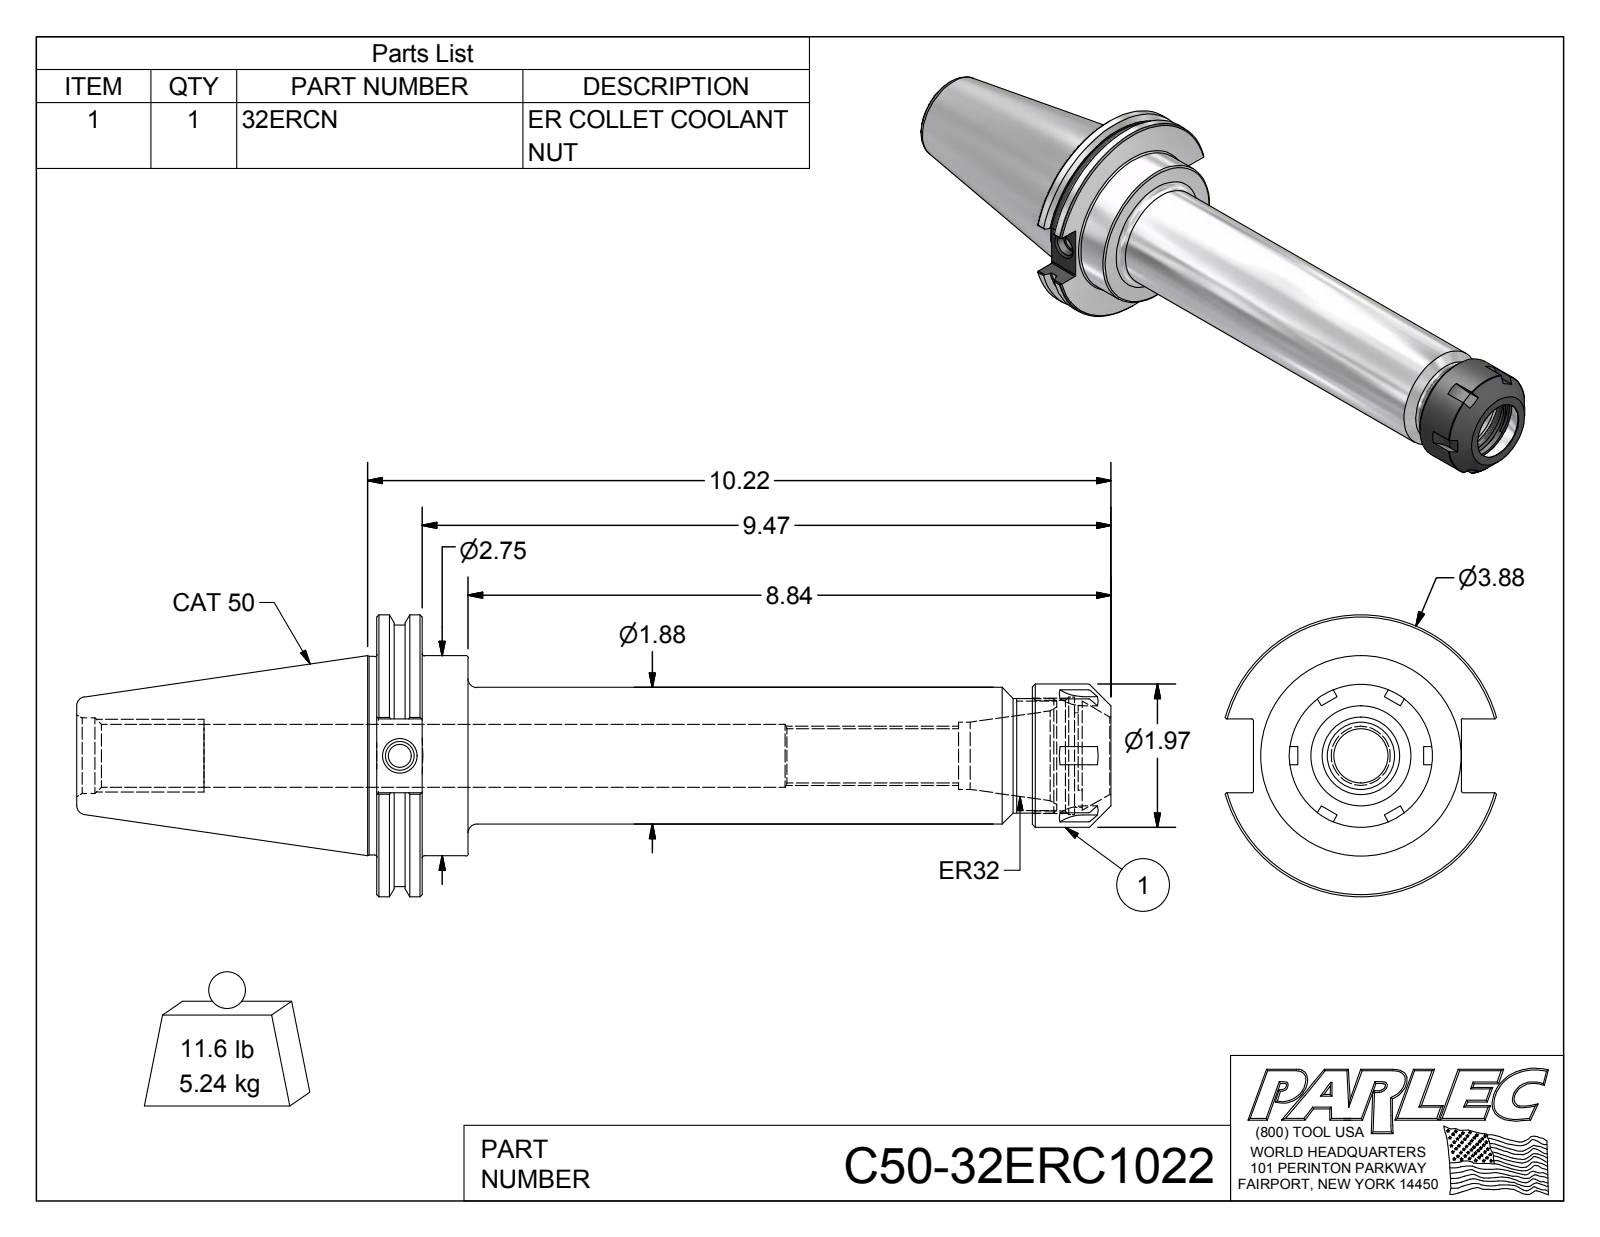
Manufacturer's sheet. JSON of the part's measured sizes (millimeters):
{"part_name": "C50-32ERC1022; C50-32ER10-1; 32ERCN", "step_written_by": "Autodesk Inventor 2012 (AUTOMOTIVE_DESIGN)", "units": "millimeters", "bodies": {"solids": 2, "faces": 125, "planar": 52, "cylindrical": 37, "other": 36}, "overall_size": [361.2, 98.4, 94.7], "volume_mm3": 673000, "surface_area_mm2": 102100, "round_holes": [[8, 1], [10.1, 1], [18.9, 1], [21.9, 1], [22, 1], [23.5, 1], [26.4, 1], [27, 1], [33, 1], [38.7, 1], [41, 1]], "round_bosses_or_shafts": [[98.4, 1], [91.3, 1], [69.9, 1], [69.3, 1], [50, 1], [47.8, 1], [40, 1]], "partial_cylinders_radius": [[0.5, 8], [12.7, 6], [17.5, 1]], "face_to_face_distances": [15.9, 31.9, 16, 228.9, 213, 197, 243.6, 227.7, 211.7, 14.7], "hole_center_spacings": [1.5]}
